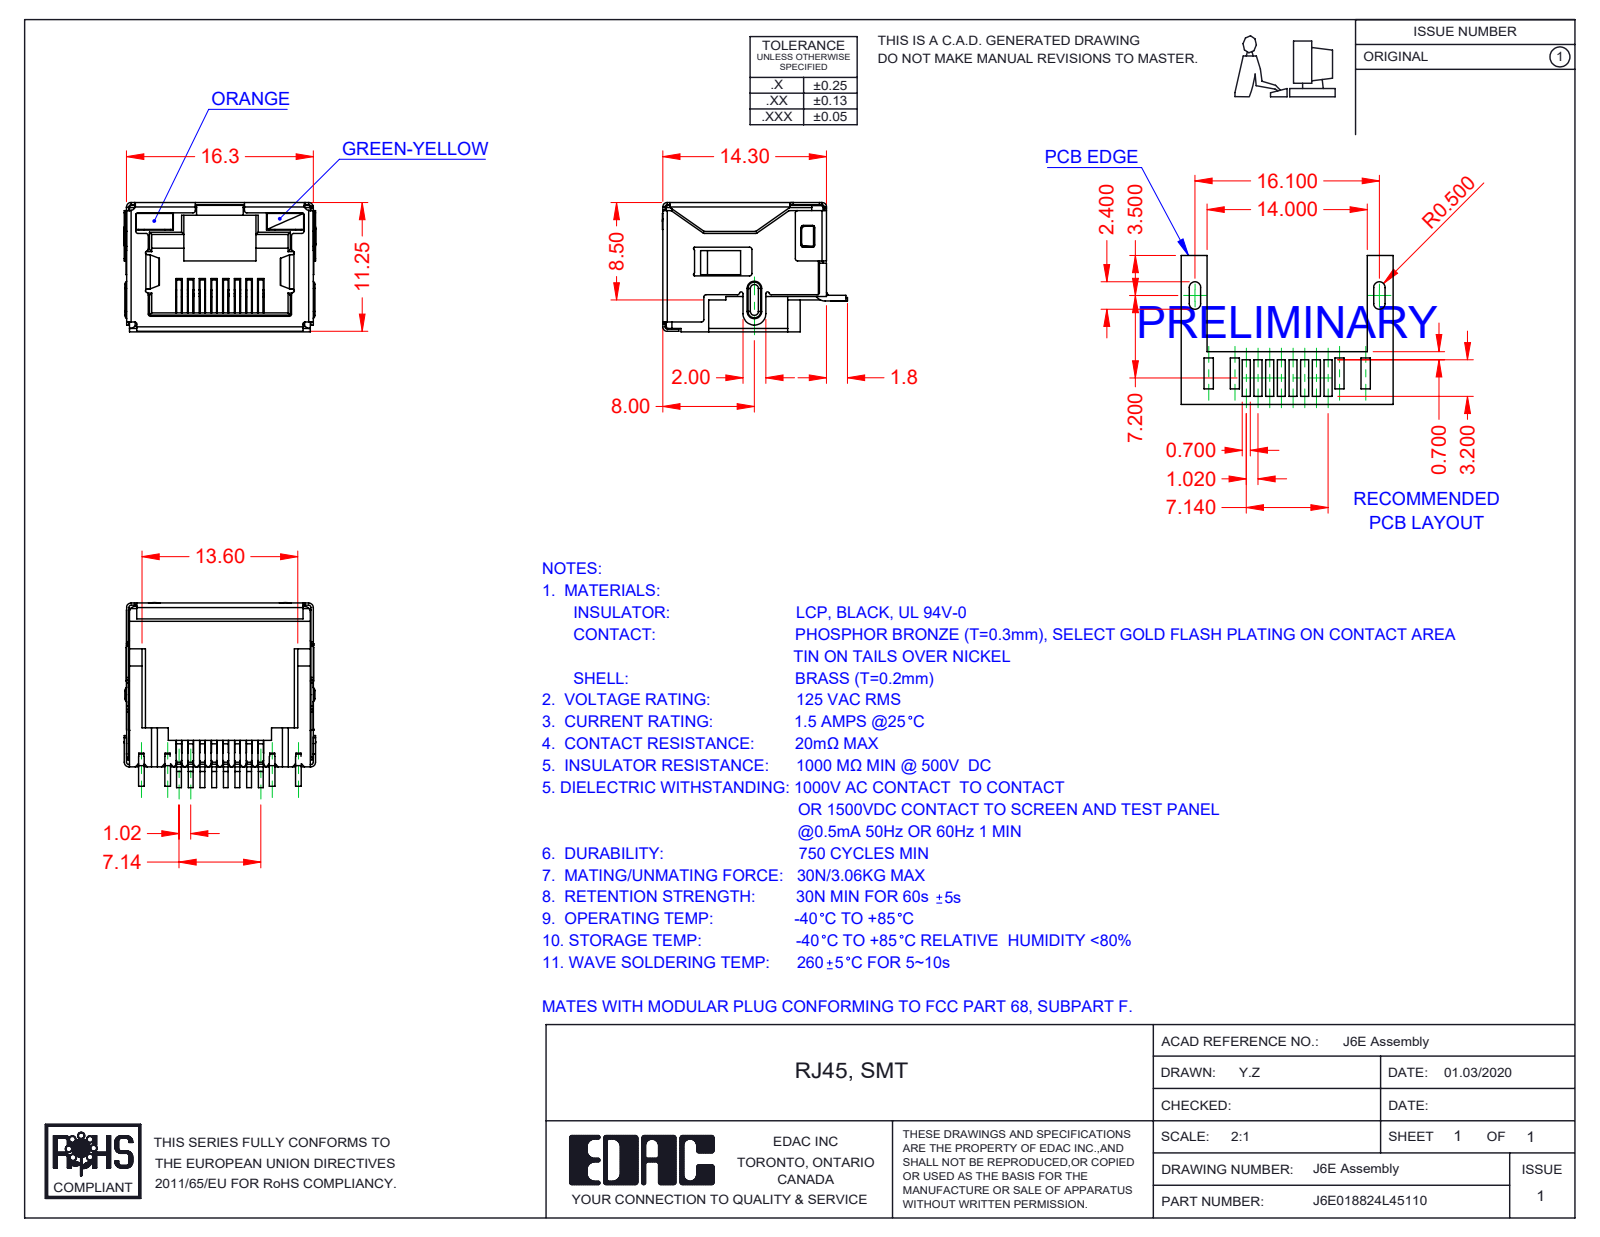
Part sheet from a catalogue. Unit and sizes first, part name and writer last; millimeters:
Units: millimetres
Overall size (bounding box): 16.75 × 16.15 × 11.3
Partial cylindrical surfaces — rounded edges, fillets, slot ends (radius × count): R0.2 ×82, R0.25 ×17, R0.4 ×13, R0.5 ×13, R0.1 ×10, R0.15 ×7, R0.3 ×4, R1 ×3
Main face-to-face distances: 11.05, 16.05, 16.1, 15.85, 11.1, 11.3, 2.4, 0.7, 9.85, 0.49
Volume: 1 109 mm³ · Surface area: 4 045 mm²
Bodies: 12 solids, 1498 faces (1099 planar, 349 cylindrical, 50 other)
Part name (STEP PRODUCT): 6E Insulator_LED; J6E018824L45110; 6E LED LH_4-Orange; 6E LED RH_5-Green-Yellow (+2 more)
STEP written by: SolidWorks 2016 (CONFIG_CONTROL_DESIGN)
